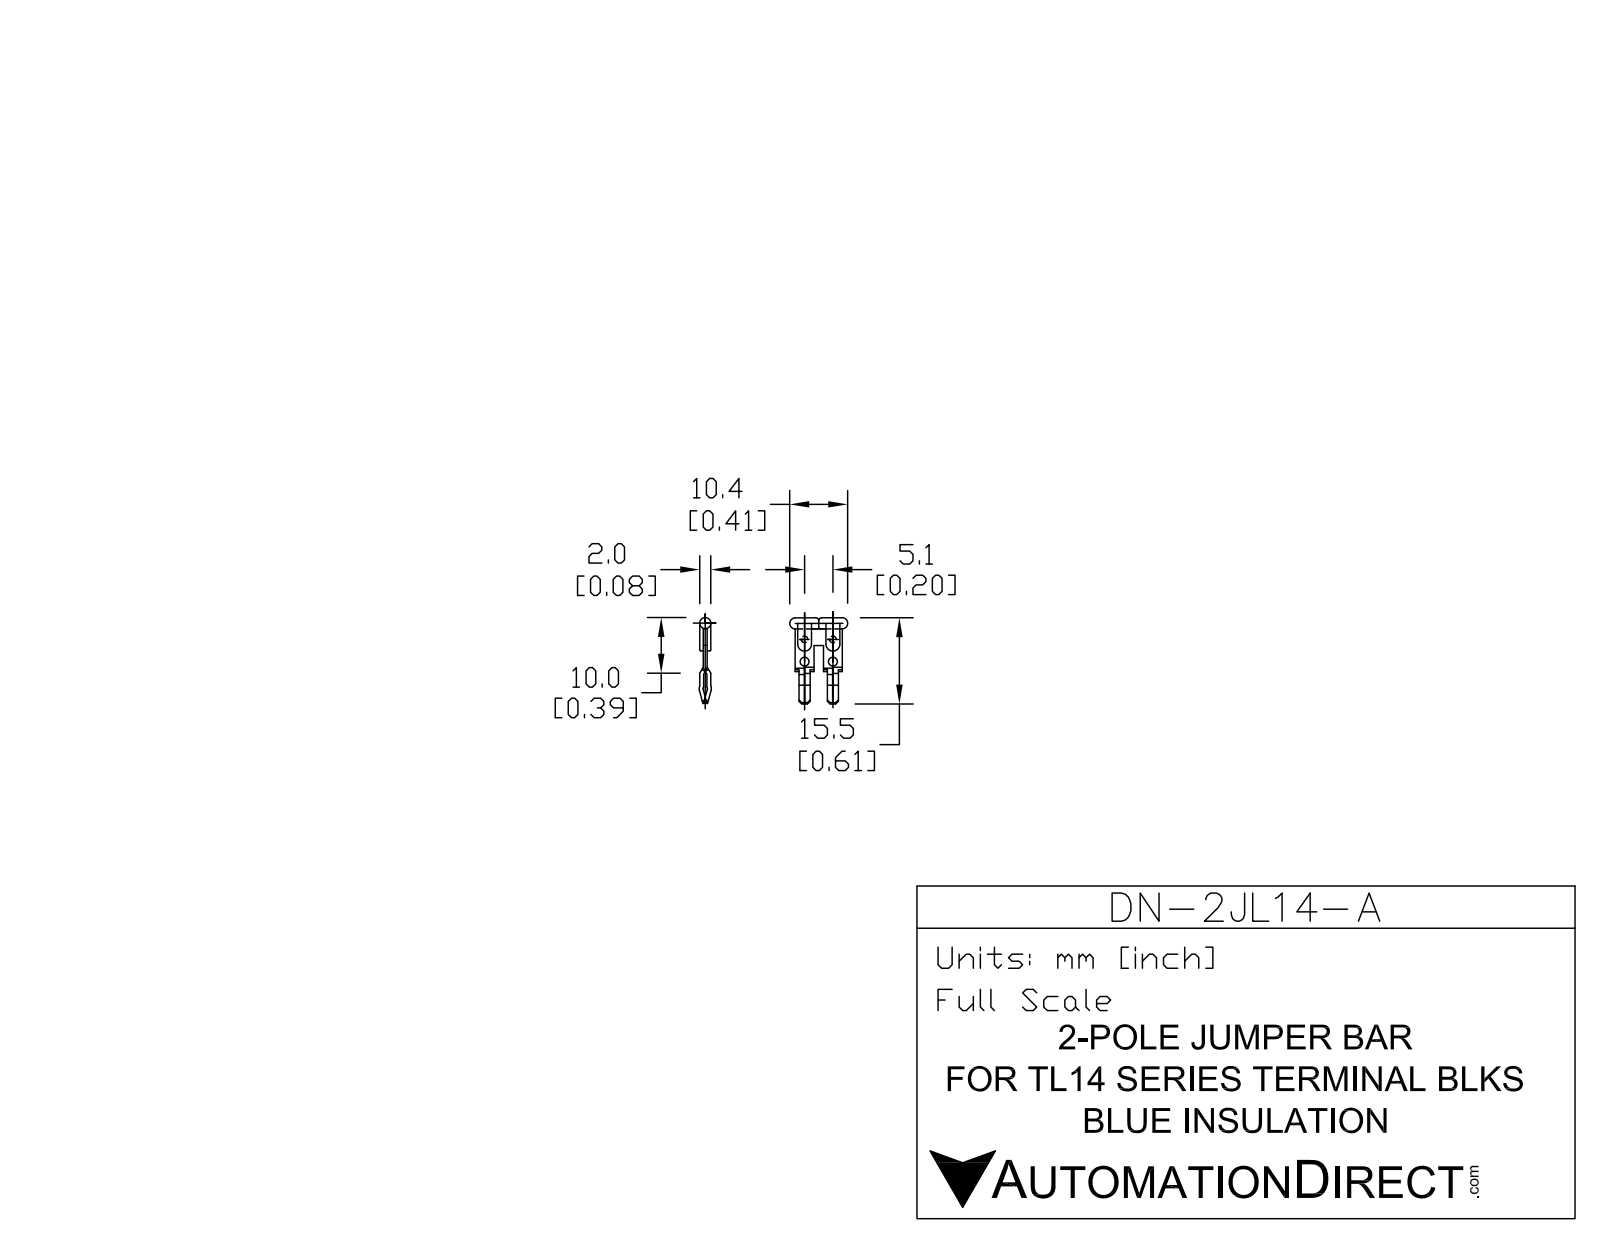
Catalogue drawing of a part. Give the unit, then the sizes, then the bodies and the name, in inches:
Units: inches
Overall size (bounding box): 0.61 × 0.398 × 0.082
Round holes (diameter × count): ⌀0.047 ×2, ⌀0.051 ×2
Round bosses / shafts (diameter × count): ⌀0.079 ×1
Partial cylindrical surfaces — rounded edges, fillets, slot ends (radius × count): R0.01 ×8, R0.019 ×4, R0.028 ×4, R0.02 ×3, R0.049 ×2
Main face-to-face distances: 0.028, 0.026, 0.053, 0.201, 0.047, 0.079, 0.022, 0.051, 0.065, 0.069
Hole centre spacings: 0.157, 0.201, 0.255
Volume: 0.008 in³ · Surface area: 0.564 in²
Bodies: 2 solids, 147 faces (79 planar, 52 cylindrical, 16 other)
Part name (STEP PRODUCT): 43531_02_RDS_DN-2JL14
STEP written by: SolidWorks 2013 (AUTOMOTIVE_DESIGN)
